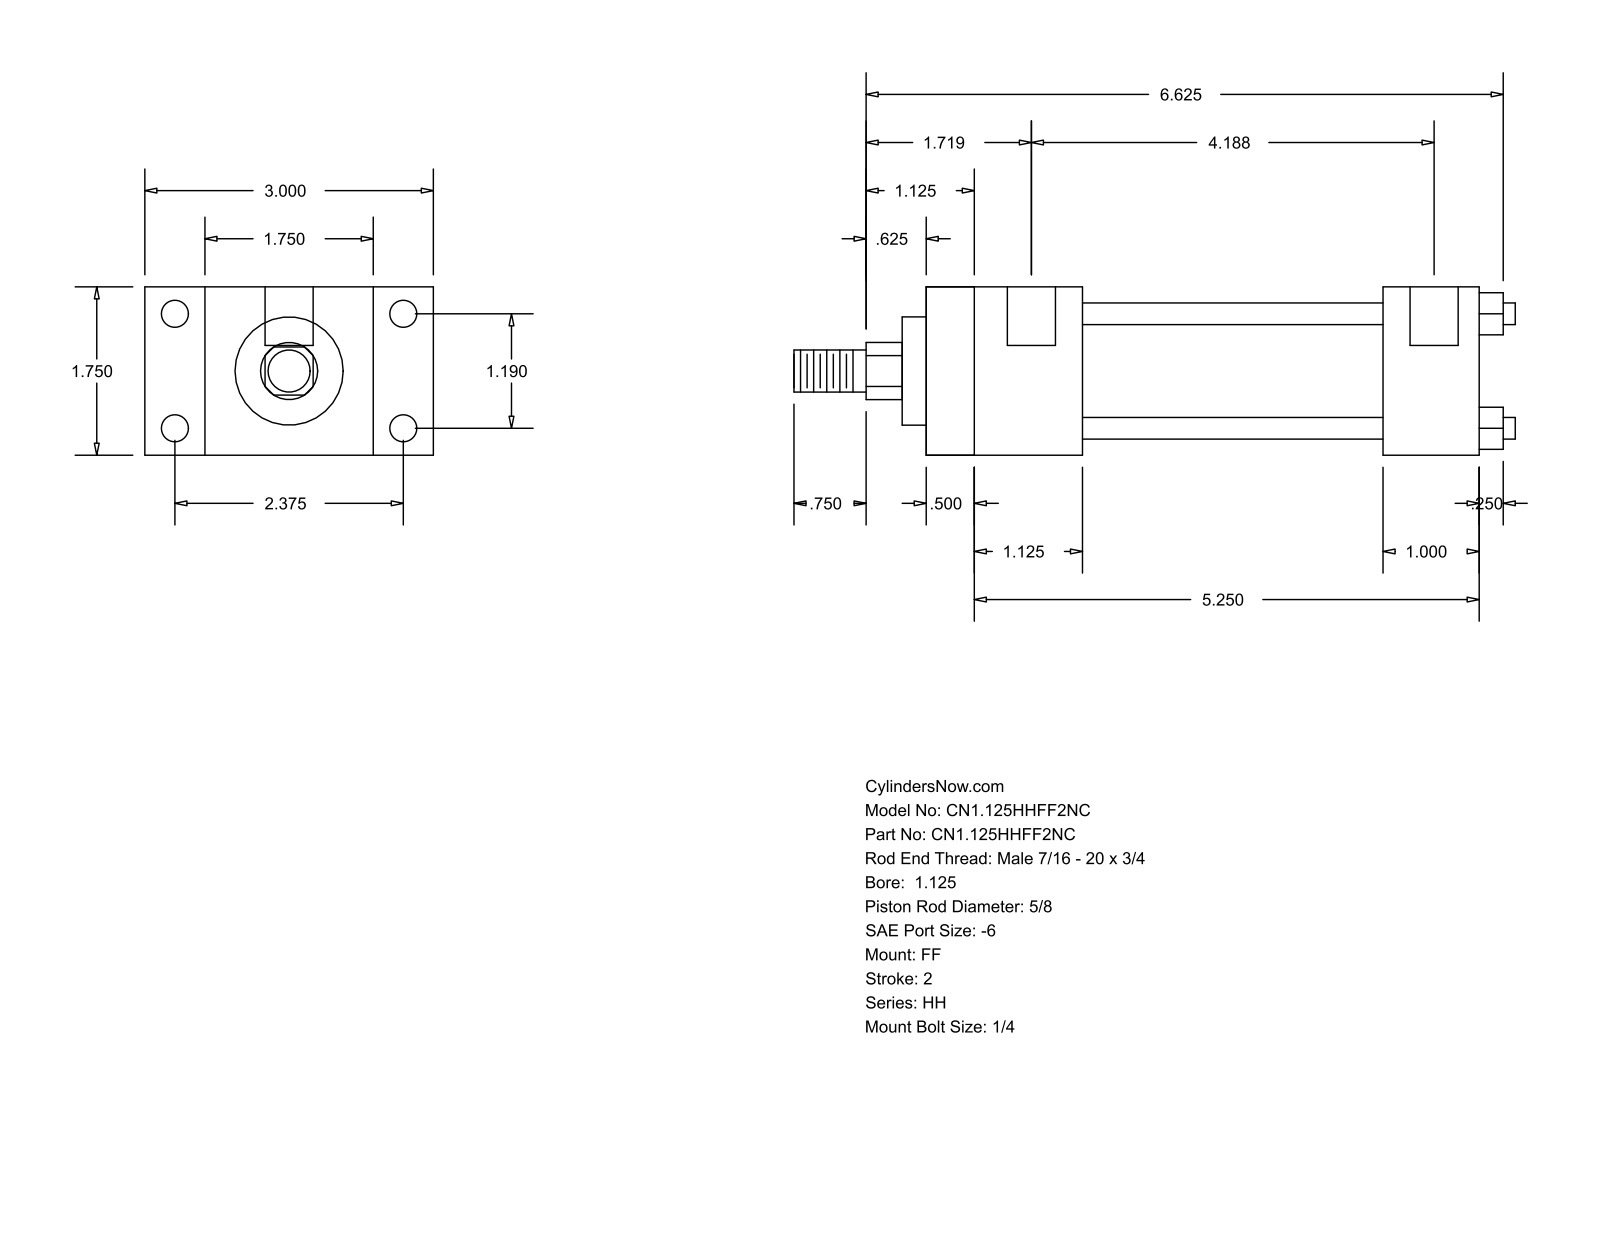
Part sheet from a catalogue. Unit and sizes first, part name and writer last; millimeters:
Units: millimetres
Overall size (bounding box): 190.5 × 76.2 × 44.45
Round holes (diameter × count): ⌀5.56 ×4, ⌀7.14 ×4, ⌀12.7 ×2
Round bosses / shafts (diameter × count): ⌀5.71 ×4, ⌀34.92 ×1, ⌀28.57 ×1, ⌀15.88 ×1, ⌀11.11 ×1
Partial cylindrical surfaces — rounded edges, fillets, slot ends (radius × count): R7.54 ×1
Main face-to-face distances: 44.46, 146.05, 15.87, 12.69, 133.36, 28.58, 60.33, 25.4, 41.27, 120.65
Hole centre spacings: 30.22, 60.32, 67.47, 103.19, 3.17, 106.36
Bodies: 0 solids, 92 faces (64 planar, 28 cylindrical, 0 other)
Part name (STEP PRODUCT): HH_FF__0112_0.625
STEP written by: GSSL Pune (CONFIG_CONTROL_DESIGN)
